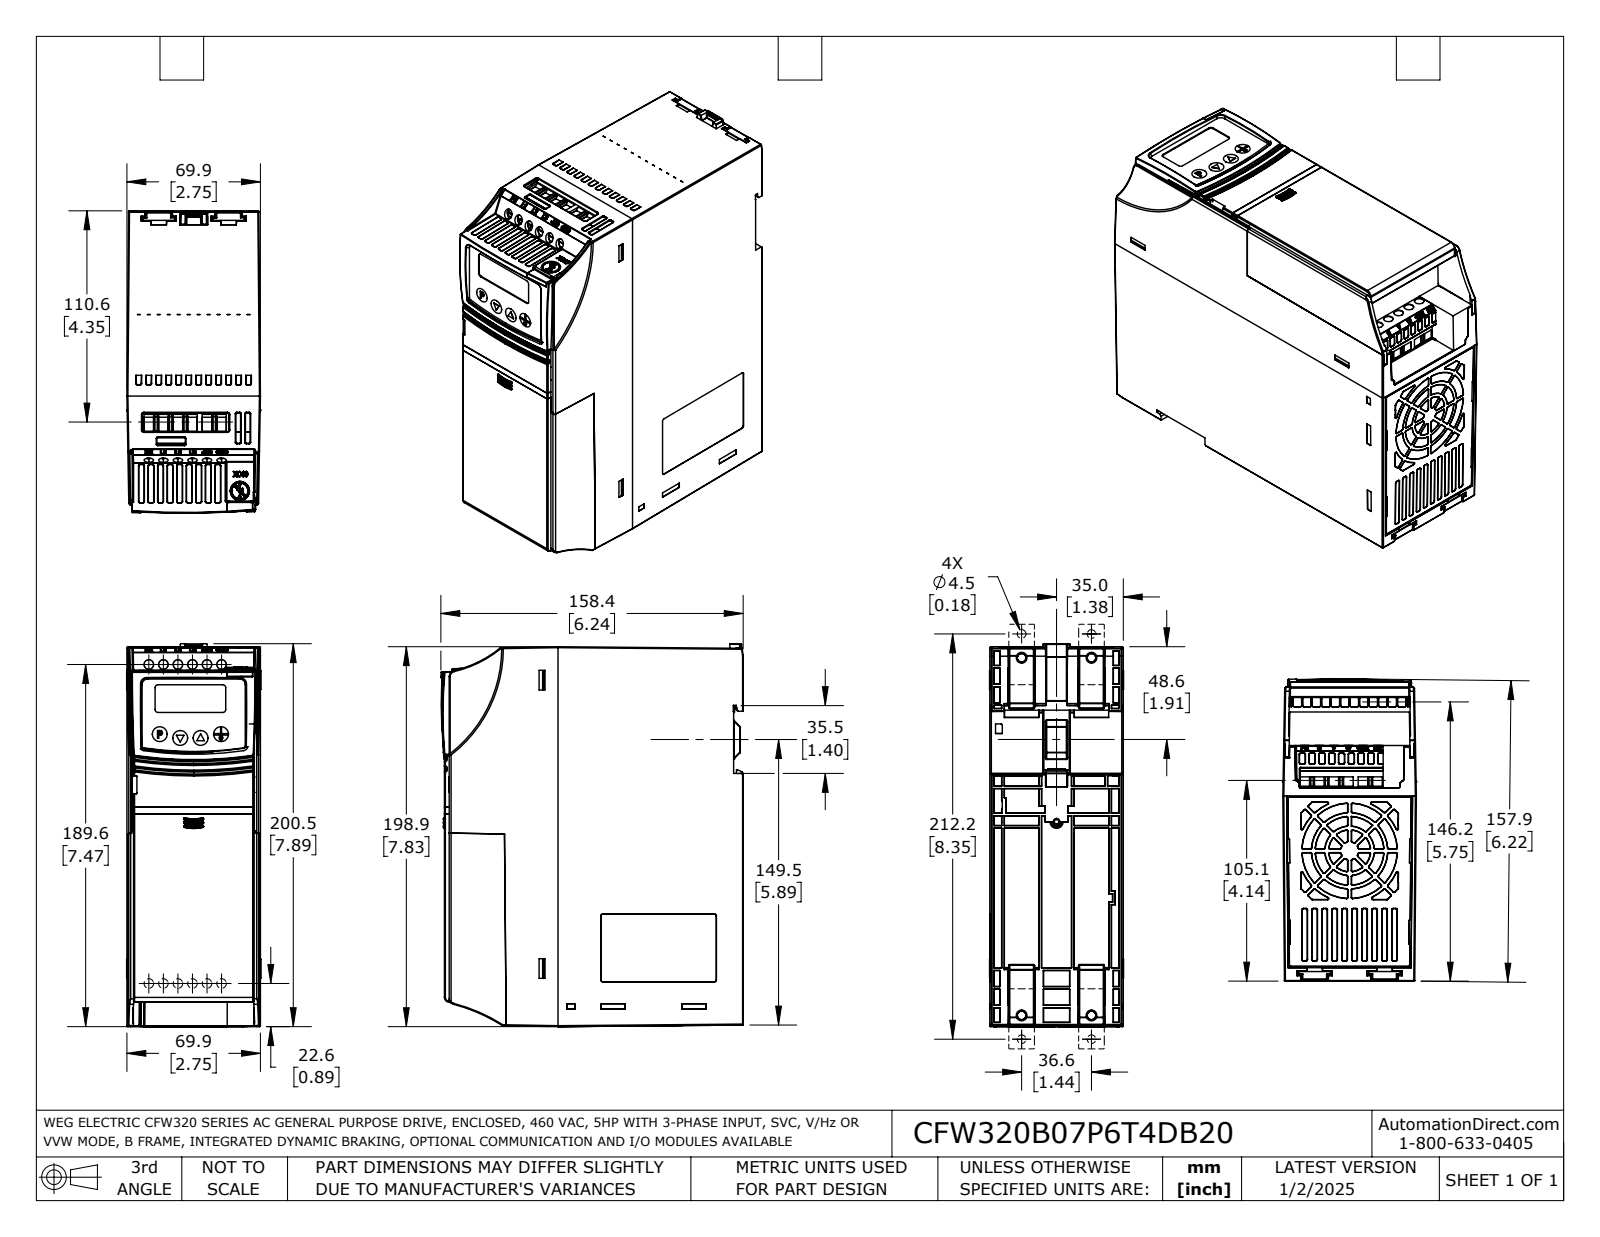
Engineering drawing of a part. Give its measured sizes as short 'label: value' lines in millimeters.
name: CFW320B07P6T4DB20
written by: SolidWorks 2021 (AUTOMOTIVE_DESIGN)
unit: mm
bodies: 5 solids, 3984 faces (1907 planar, 899 cylindrical, 1178 other)
size: 200.5 × 158.4 × 70.2
volume: 401 600 mm³; area: 248 500 mm²
holes: 6× ⌀4.9
rounds: 355× R0.3, 181× R0.5, 14× R1, 7× R0.8, 5× R3, 2× R0.3, 2× R2.8, 1× R2.5
face distances: 5.3, 2.5, 2.5, 148, 145.5, 5.4, 150.9, 153.3, 190.5, 1
hole spacings: 7.6, 15.2, 22.9, 30.5, 38.1
